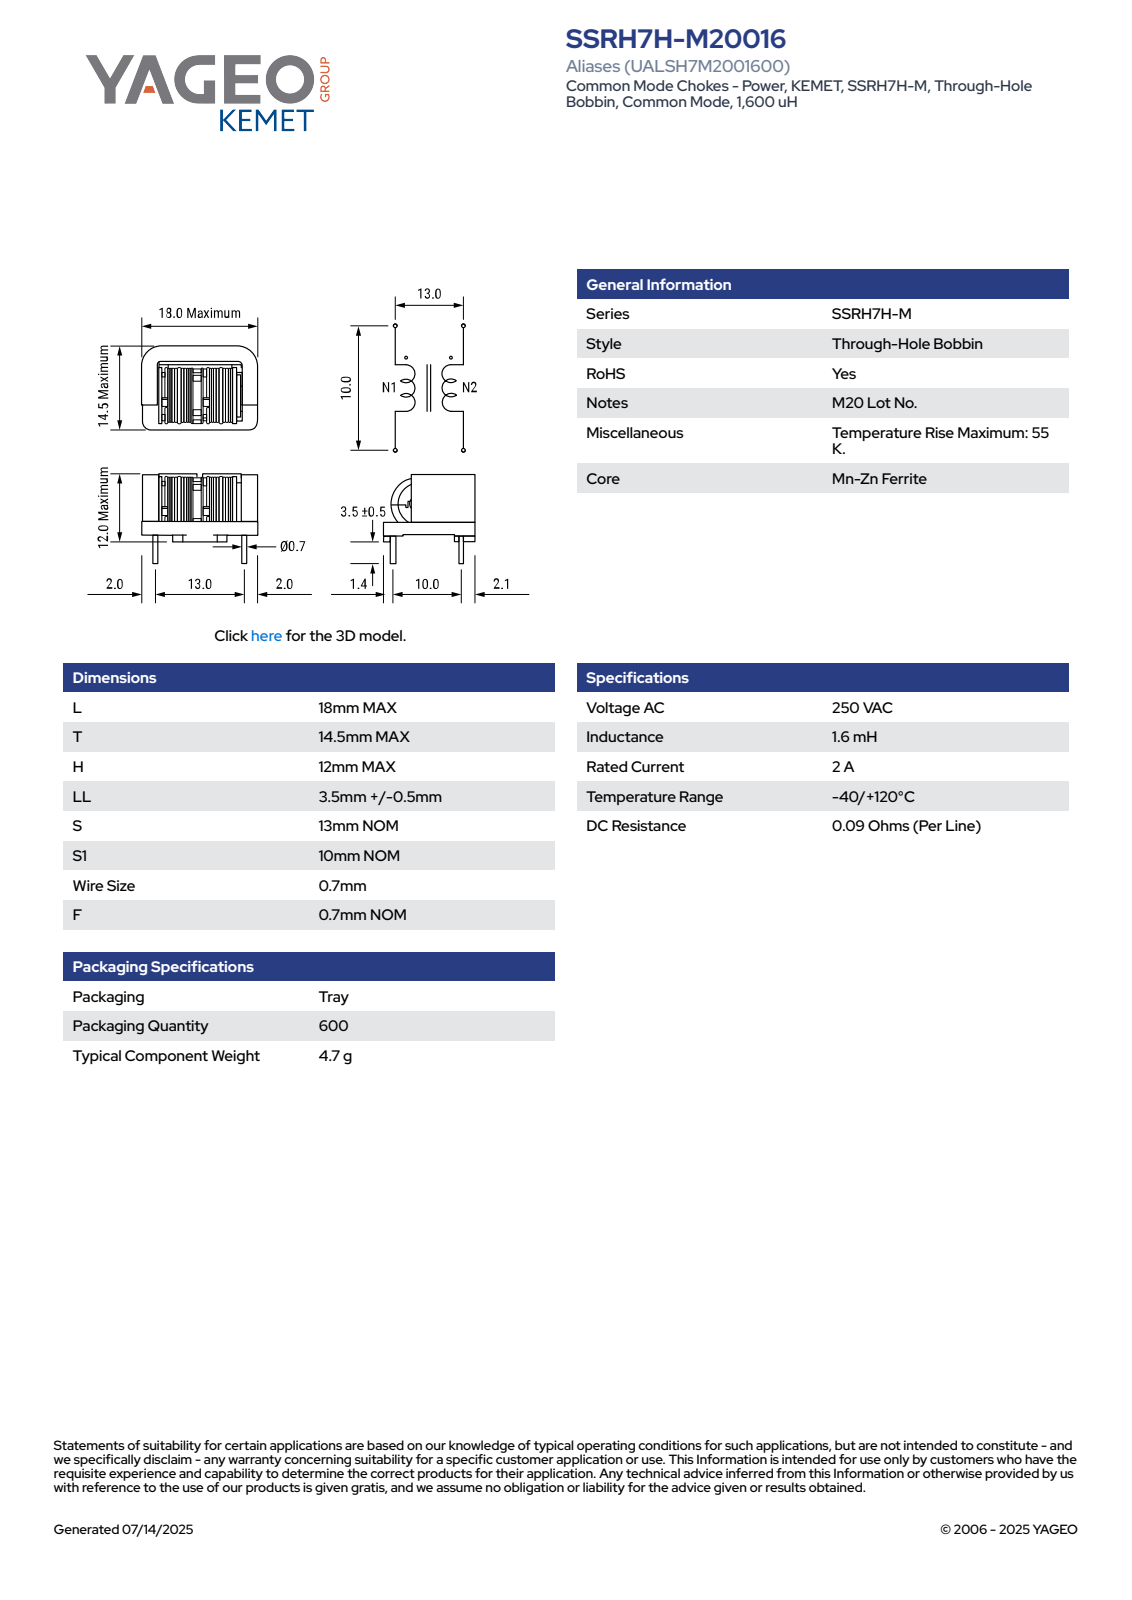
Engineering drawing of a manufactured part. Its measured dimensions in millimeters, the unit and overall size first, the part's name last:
Units: millimetres
Overall size (bounding box): 18 × 15.5 × 14.5
Round holes (diameter × count): ⌀3.5 ×1
Round bosses / shafts (diameter × count): ⌀0.7 ×4, ⌀9 ×1, ⌀7 ×1, ⌀6 ×1
Partial cylindrical surfaces — rounded edges, fillets, slot ends (radius × count): R0.5 ×10, R0.2 ×6, R0.1 ×2, R1 ×2, R2 ×2, R3.3 ×2, R1.65 ×1, R2.35 ×1
Main face-to-face distances: 3.5, 2.8, 15.2, 0.6, 11, 0.69, 2.81, 2.9, 6, 1.2
Volume: 1 856 mm³ · Surface area: 2 362 mm²
Bodies: 1 solid, 332 faces (203 planar, 105 cylindrical, 24 other)
Part name (STEP PRODUCT): SSRH7H(MAX-LOGO)
STEP written by: SolidWorks 2018 (AUTOMOTIVE_DESIGN)
